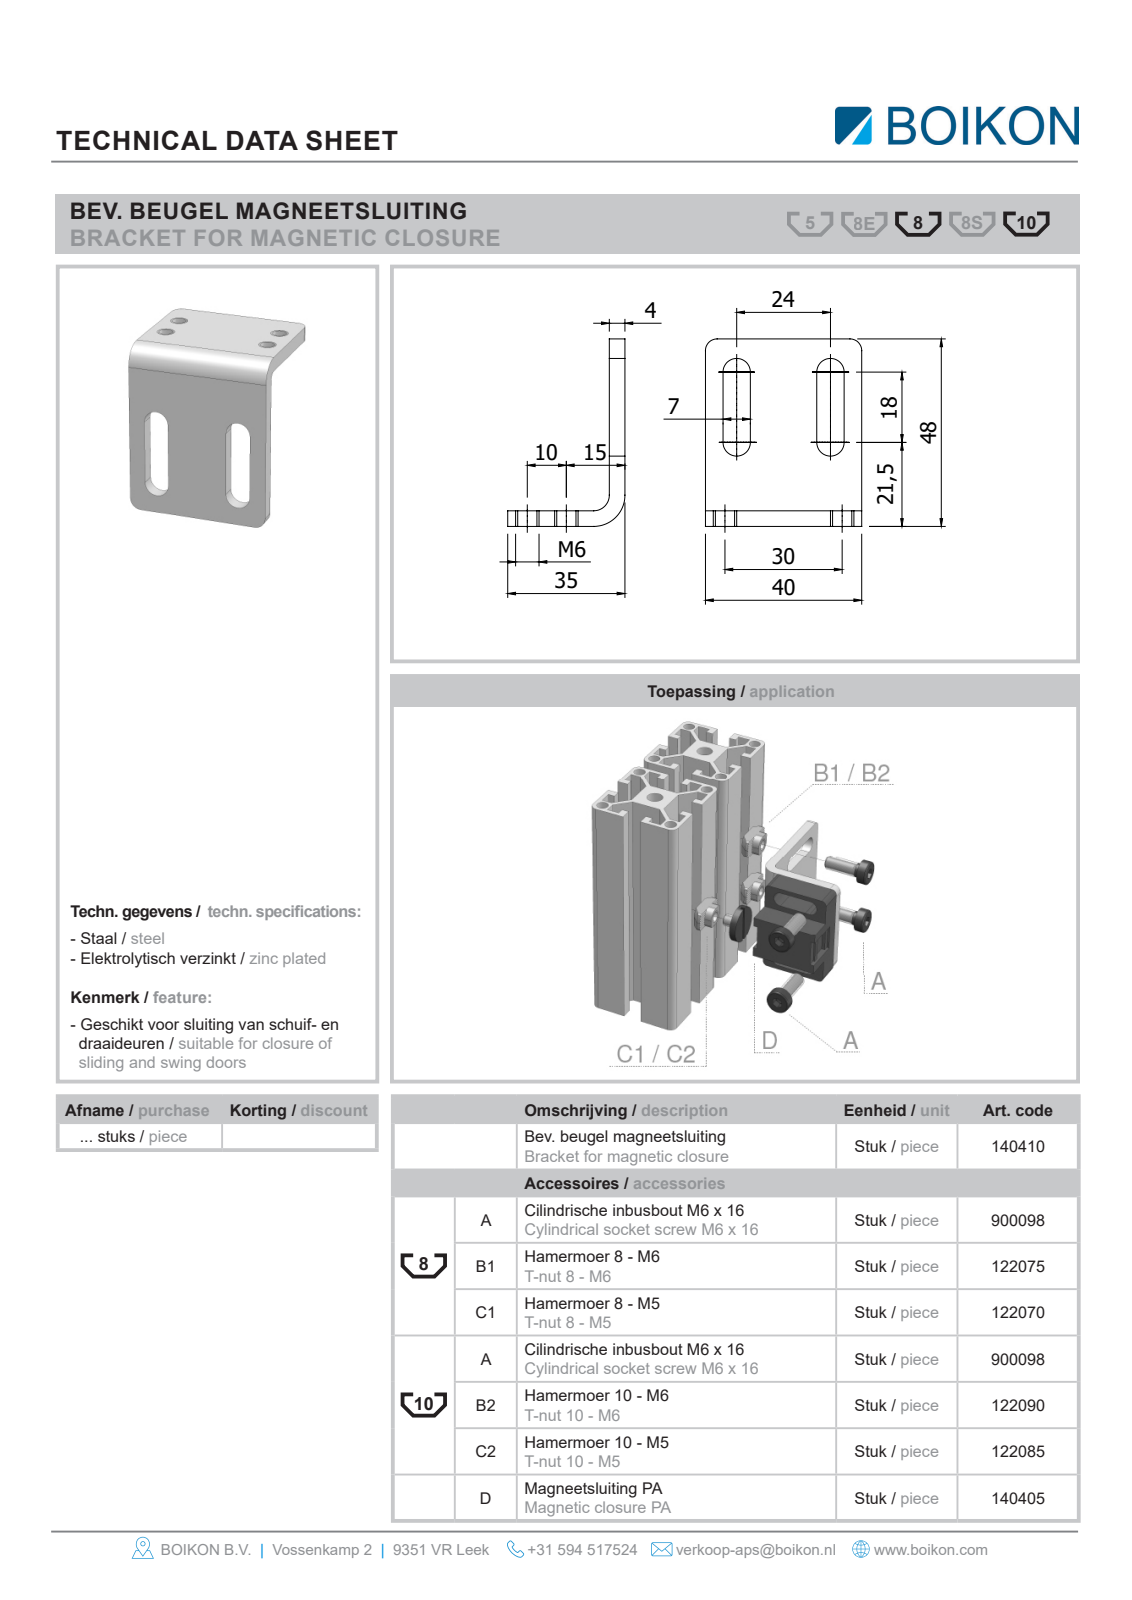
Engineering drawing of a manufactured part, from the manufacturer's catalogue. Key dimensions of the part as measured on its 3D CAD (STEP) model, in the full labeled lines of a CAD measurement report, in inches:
Part name (STEP PRODUCT): Root; 140410Bevestigingsbeugel voor magneetsluitingBOIKON
STEP written by: HiCAD 2013 1802.4 Build 509 (AUTOMOTIVE_DESIGN)
Units: inches
Bodies: 1 solid, 26 faces (12 planar, 14 cylindrical, 0 other)
Overall size (bounding box): 1.89 × 1.575 × 1.378
Volume: 0.653 in³ · Surface area: 10.83 in²
Round holes (diameter × count): ⌀0.197 ×4
Partial cylindrical surfaces — rounded edges, fillets, slot ends (radius × count): R0.118 ×4, R0.138 ×4, R0.079 ×1, R0.236 ×1
Main face-to-face distances: 0.157, 1.575, 1.22, 0.177, 0.453, 1.122, 1.398, 0.276, 0.945, 1.89
Hole centre spacings: 0.394, 1.181, 1.245
